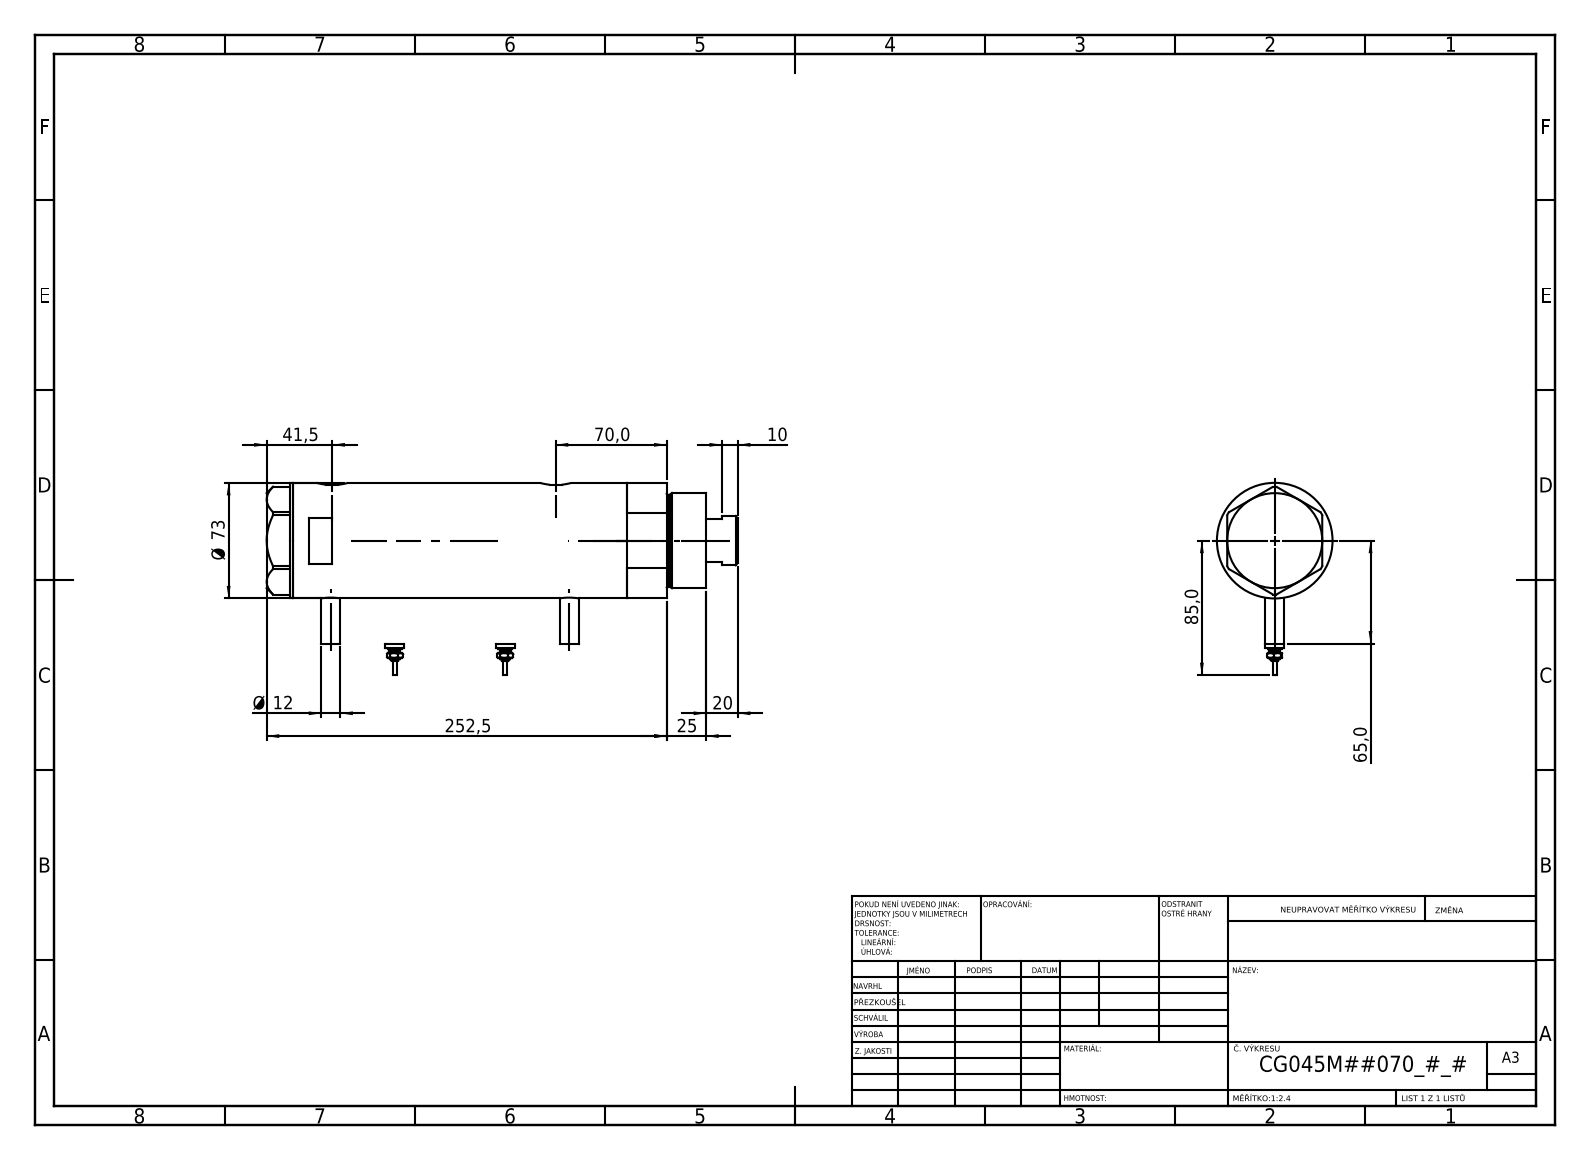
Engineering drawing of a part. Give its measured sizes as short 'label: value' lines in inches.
name: V270CG_VC; V270CG_MIDDLE; Switch; V270CG_FRONT (+1 more)
written by: SolidWorks 2019 (CONFIG_CONTROL_DESIGN)
unit: in
bodies: 6 solids, 212 faces (77 planar, 71 cylindrical, 64 other)
size: 11.713 × 4.783 × 2.874
volume: 64.99 in³; area: 269.6 in²
holes: 2× ⌀0.492, 2× ⌀0.518, 1× ⌀0.413, 1× ⌀1.26, 1× ⌀1.319, 1× ⌀1.772, 1× ⌀1.89, 1× ⌀2.52
bosses: 4× ⌀0.472, 2× ⌀0.354, 2× ⌀0.276, 2× ⌀0.177, 2× ⌀0.098, 1× ⌀2.874, 1× ⌀2.362, 1× ⌀2.283
rounds: 2× R0.394
face distances: 5.512, 6.535, 1.024, 0.65, 1.673, 7.185, 2.756, 0.079, 10.276, 10.925
hole spacings: 0.039, 0.335, 5.551, 5.591, 5.886, 5.925
